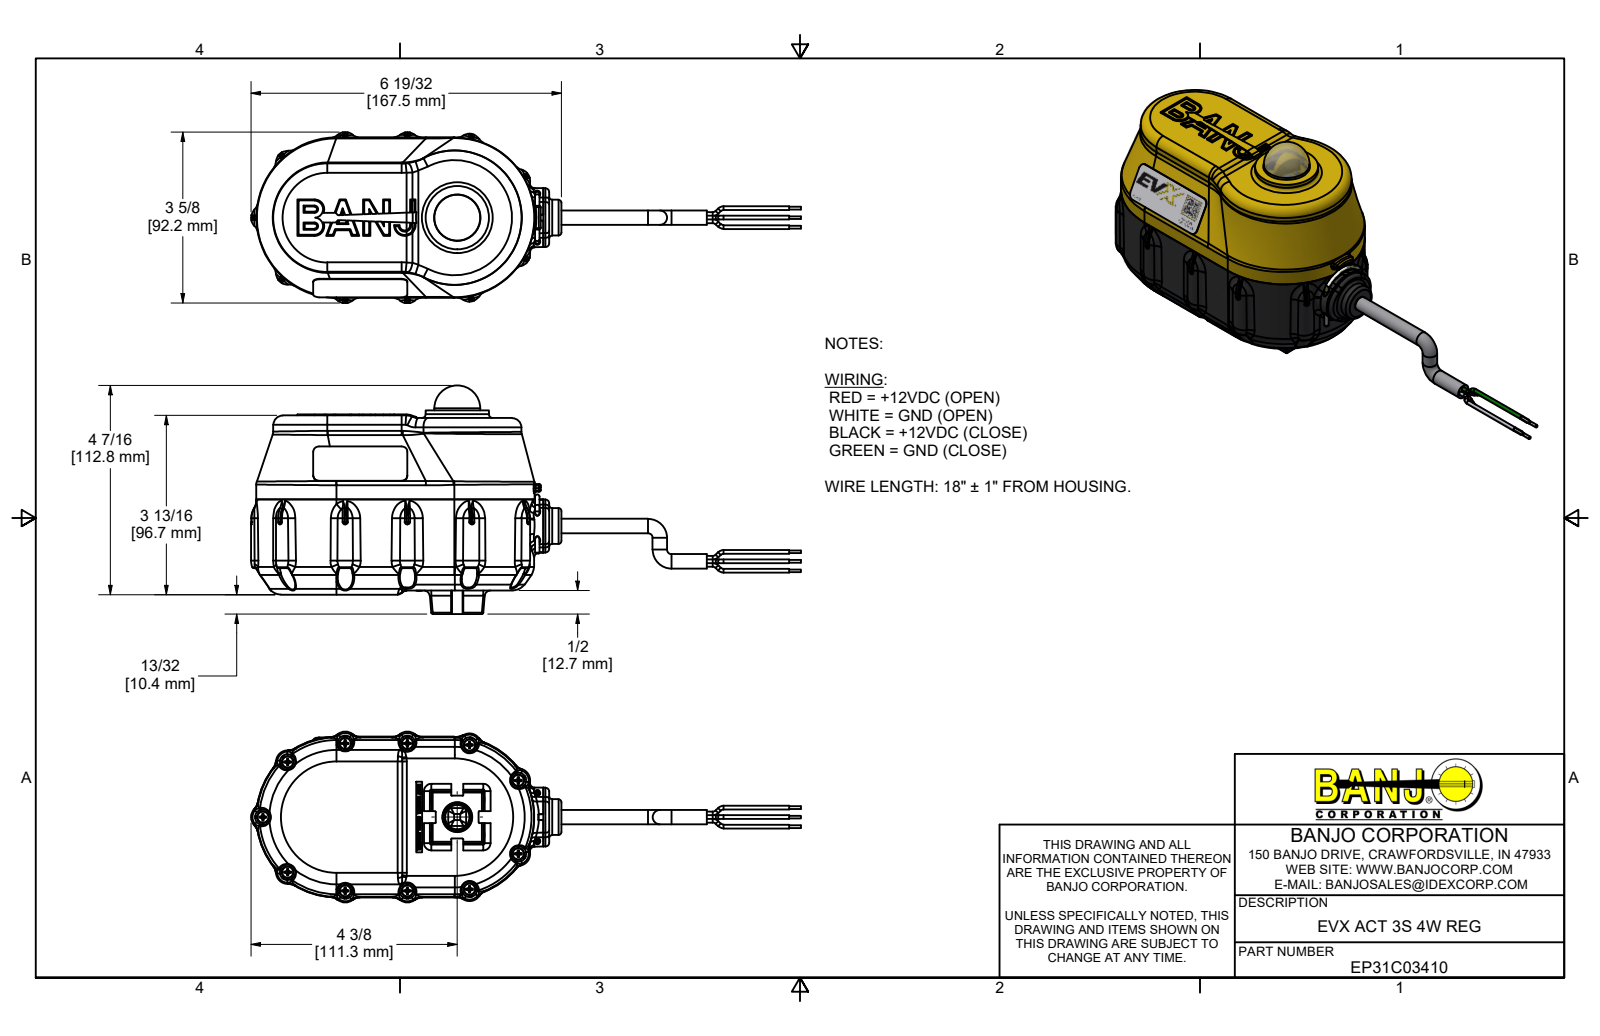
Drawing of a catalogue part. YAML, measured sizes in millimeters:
part_name: "EP31C03410; 91400A119; 95584A200; 95584A201 (+8 more)"
step_written_by: "Autodesk Inventor 2022 (AUTOMOTIVE_DESIGN)"
units: millimeters
bodies: {solids: 71, faces: 11533, planar: 3348, cylindrical: 2978, other: 5207}
overall_size: [296.8, 123.3, 92.2]
volume: 508200
surface_area: 256000
round_holes:
  - {diameter: 3.8, count: 13}
  - {diameter: 2.4, count: 11}
  - {diameter: 2.7, count: 4}
  - {diameter: 3.2, count: 4}
  - {diameter: 3.5, count: 4}
  - {diameter: 4.3, count: 4}
  - {diameter: 2.3, count: 2}
  - {diameter: 2.7, count: 2}
  - {diameter: 2.9, count: 2}
  - {diameter: 3, count: 2}
  - {diameter: 3.1, count: 2}
  - {diameter: 3.3, count: 2}
round_bosses_or_shafts:
  - {diameter: 2, count: 20}
  - {diameter: 6.4, count: 17}
  - {diameter: 3.6, count: 11}
  - {diameter: 2.7, count: 11}
  - {diameter: 2.2, count: 11}
  - {diameter: 1.5, count: 8}
  - {diameter: 6.9, count: 4}
  - {diameter: 5.6, count: 4}
partial_cylinders:
  - {radius: 1, count: 147}
  - {radius: 0.5, count: 105}
  - {radius: 0.3, count: 58}
  - {radius: 0.1, count: 47}
  - {radius: 0.4, count: 40}
  - {radius: 0.8, count: 31}
  - {radius: 2, count: 28}
  - {radius: 2.5, count: 22}
face_to_face_distances: [2.5, 65.2, 42.8, 19.8, 62.6, 22.4, 0.9, 25.1, 76.3, 1.4]
hole_center_spacings: [32.6, 69.3, 75.4, 87.6, 12.4, 12.5, 17, 31.2]
